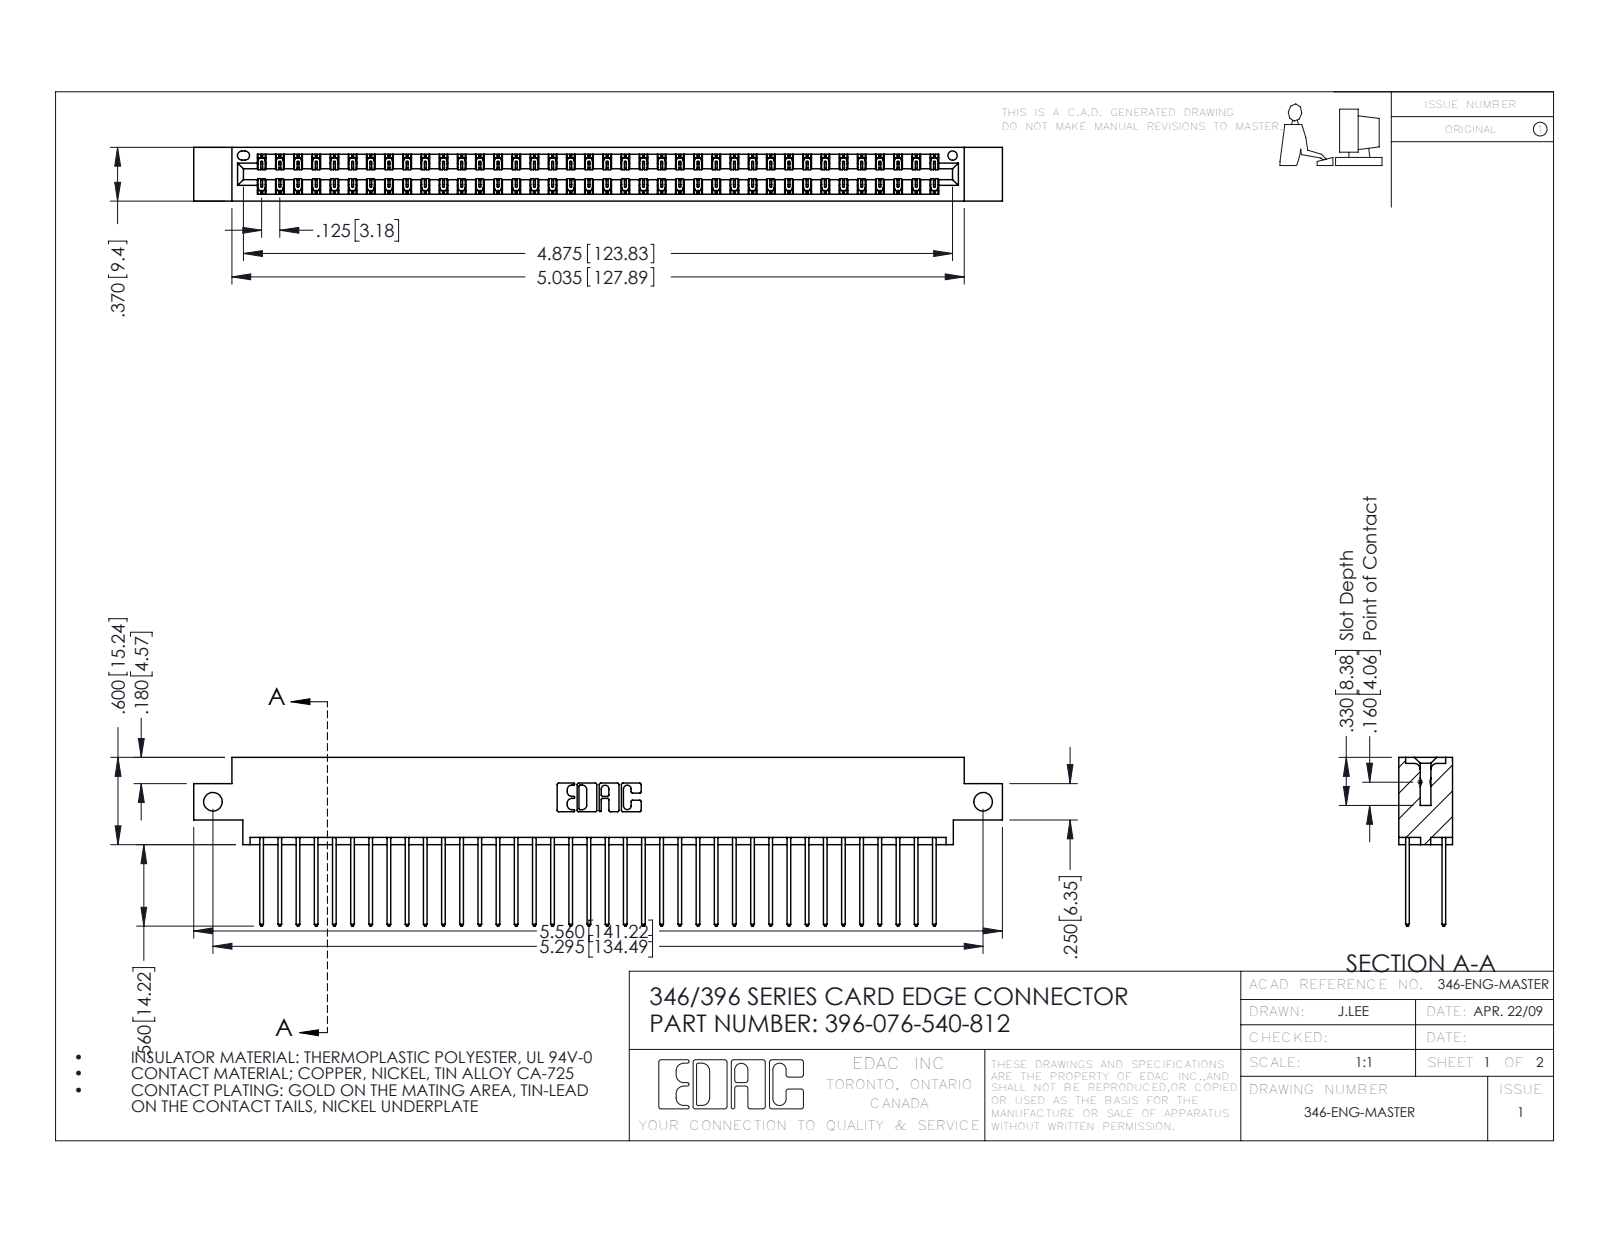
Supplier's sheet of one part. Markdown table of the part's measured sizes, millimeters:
| quantity | value |
| --- | --- |
| part name | 346 Part_0.170 Offset - Side Mount; 345-292-001_345-293-140; 396-076-540-812 |
| STEP written by | SolidWorks 2016 (CONFIG_CONTROL_DESIGN) |
| units | millimeters |
| bodies | 77 solids, 4078 faces (2740 planar, 1338 cylindrical, 0 other) |
| overall size | 141.2 × 29.5 × 9.4 |
| volume | 13 800 mm³ |
| surface area | 20 290 mm² |
| round holes (diameter × count) | 3.3 × 2, 1.6 × 1 |
| partial cylindrical surfaces (radius × count) | 0.2 × 114, 0.3 × 76, 0.3 × 22, 0.2 × 6, 0.8 × 6, 0.7 × 3, 0.4 × 2, 0.6 × 2 |
| main face-to-face distances | 1.2, 8.2, 6.4, 1.8, 7.6, 0.6, 9.4, 7, 3.8, 5.6 |
| hole center spacings | 134.5 |
